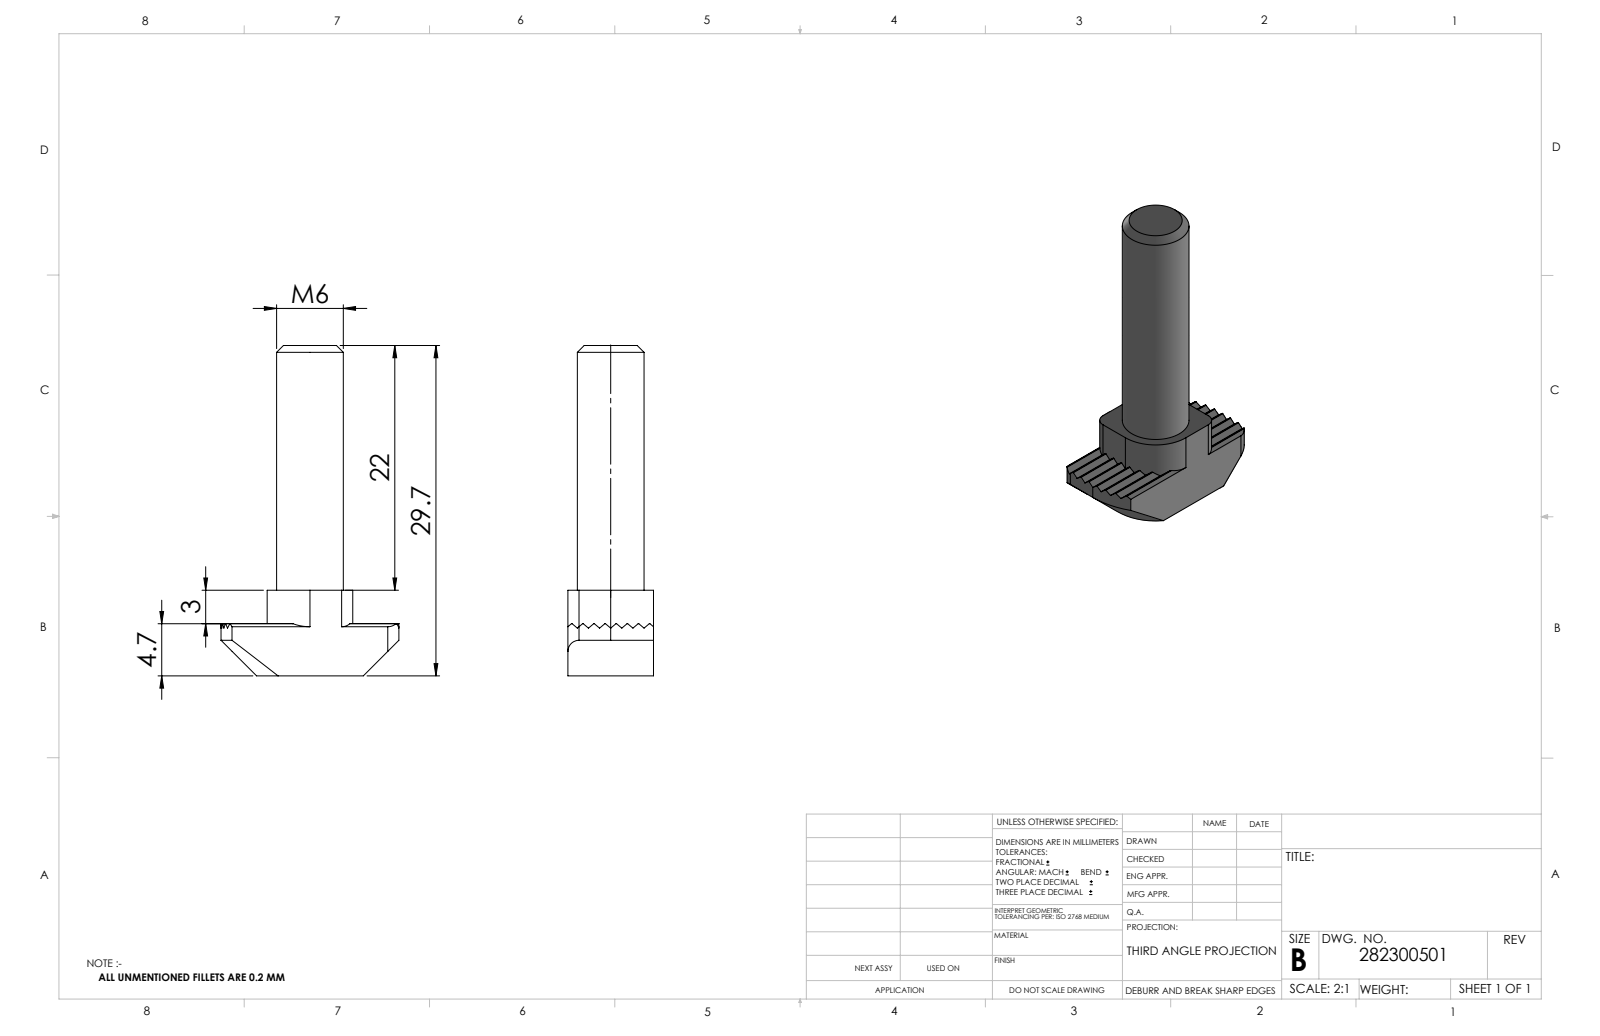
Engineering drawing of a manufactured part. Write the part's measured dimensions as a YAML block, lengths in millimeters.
part_name: "282300501"
step_written_by: "SolidWorks 2014 (CONFIG_CONTROL_DESIGN)"
units: millimeters
bodies: {solids: 1, faces: 71, planar: 41, cylindrical: 26, other: 4}
overall_size: [29.7, 16, 7.7]
volume: 1248
surface_area: 904
round_bosses_or_shafts:
  - {diameter: 6, count: 1}
partial_cylinders:
  - {radius: 1, count: 4}
  - {radius: 3.85, count: 1}
  - {radius: 8, count: 1}
face_to_face_distances: [7.7, 0.65, 1.3, 3.24, 2.59, 1.94, 1.29, 1.95, 3.89, 29.7]
